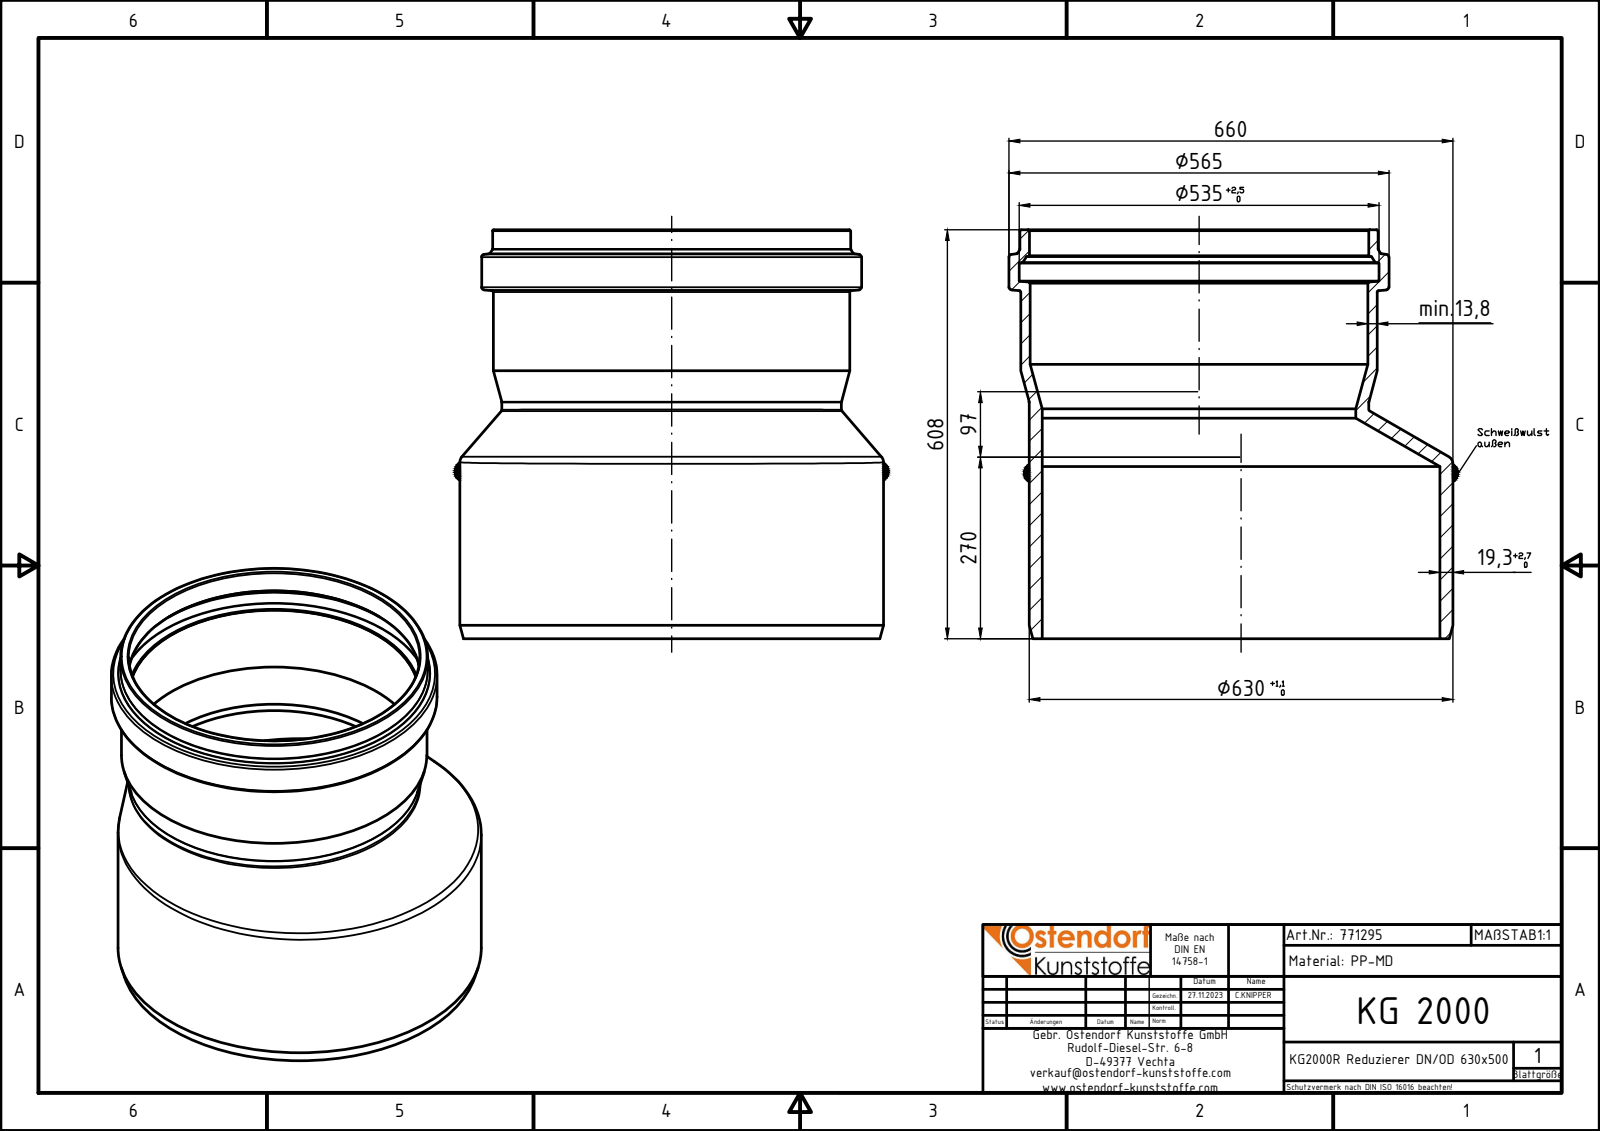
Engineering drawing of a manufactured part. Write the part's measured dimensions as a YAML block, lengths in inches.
part_name: "771295z"
step_written_by: "Autodesk Inventor 2024 (AUTOMOTIVE_DESIGN)"
units: inches
bodies: {solids: 1, faces: 43, planar: 3, cylindrical: 11, other: 29}
overall_size: [25.984, 24.803, 23.937]
volume: 1245
surface_area: 3686
round_holes:
  - {diameter: 18.362, count: 1}
  - {diameter: 19.764, count: 1}
  - {diameter: 19.803, count: 1}
  - {diameter: 19.862, count: 1}
  - {diameter: 21.063, count: 1}
  - {diameter: 23.283, count: 1}
round_bosses_or_shafts:
  - {diameter: 24.803, count: 1}
  - {diameter: 22.244, count: 1}
  - {diameter: 20.965, count: 1}
  - {diameter: 20.866, count: 1}
  - {diameter: 19.882, count: 1}
face_to_face_distances: [23.937, 20.814, 3.123]
hole_center_spacings: [2.461]
